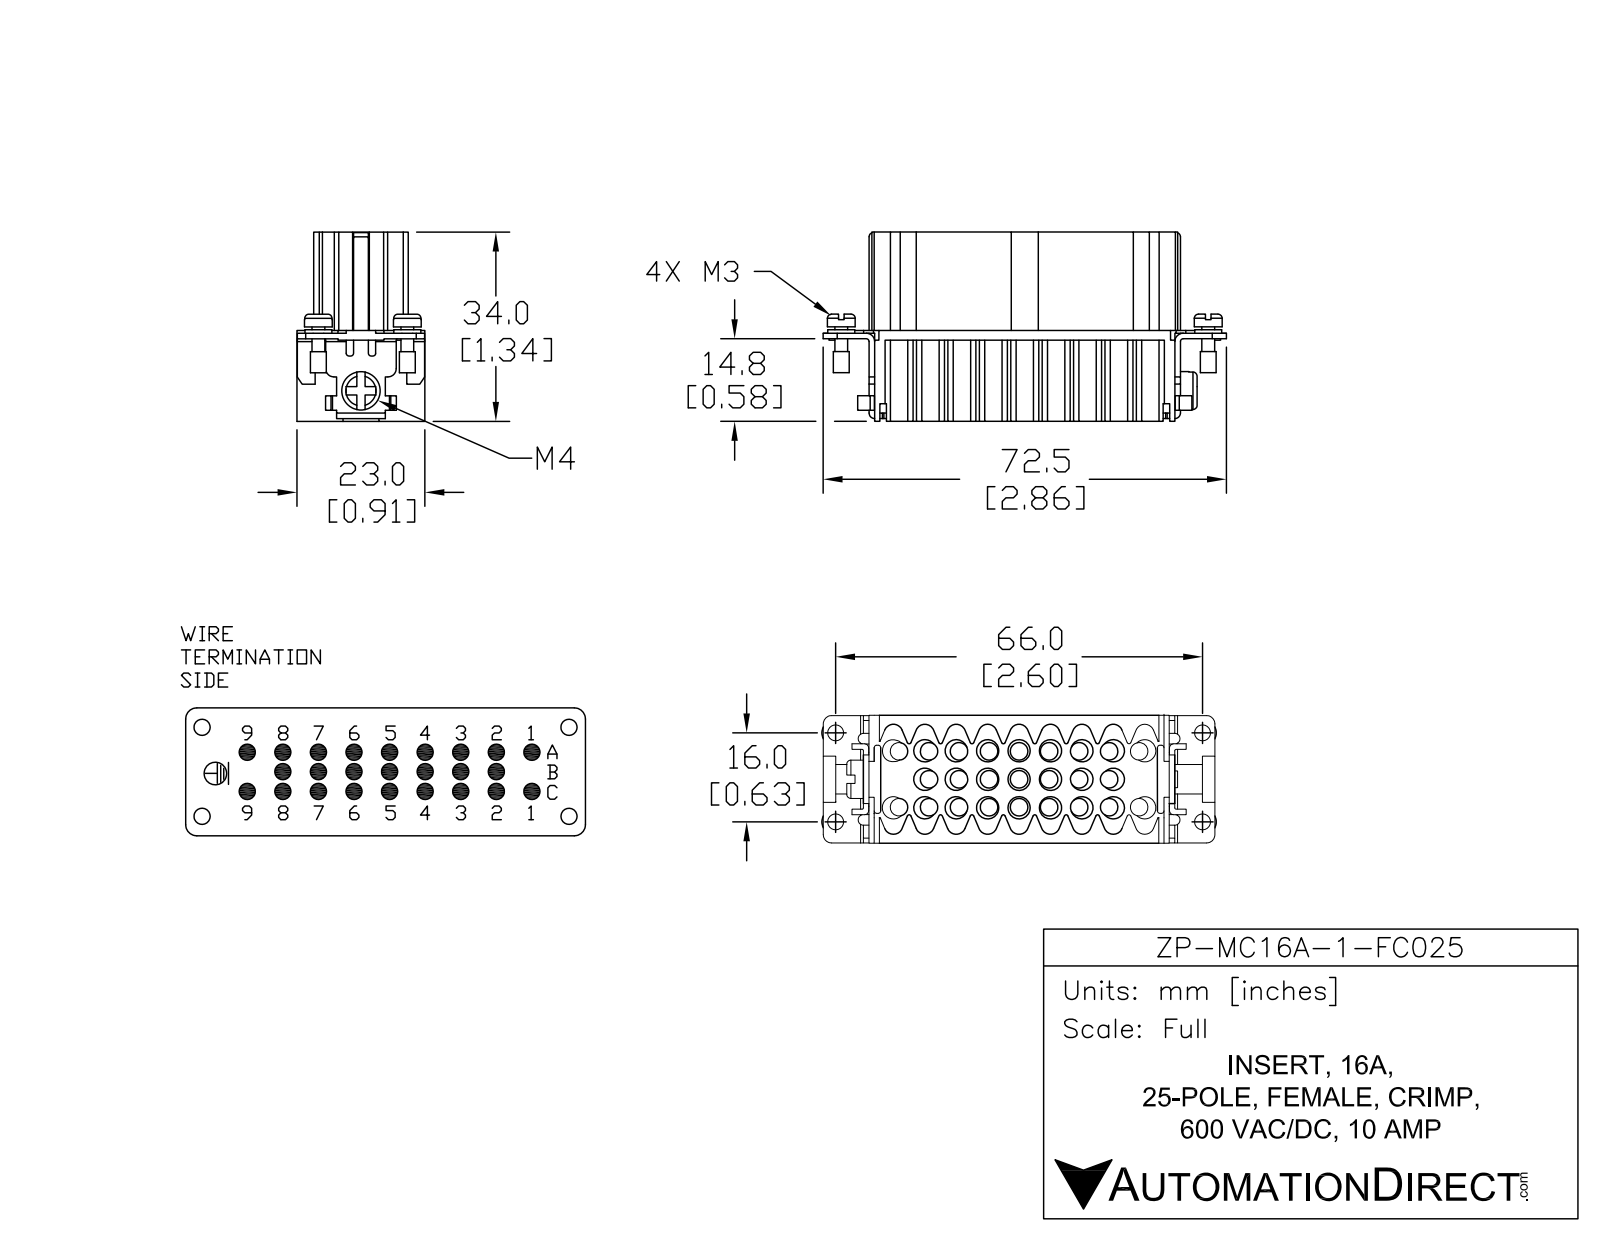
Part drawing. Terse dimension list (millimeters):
name: ZP-MC16A-1-FC025
written by: SolidWorks 2014 (AUTOMOTIVE_DESIGN)
unit: mm
bodies: 2 solids, 725 faces (395 planar, 315 cylindrical, 15 other)
size: 71 × 34.75 × 23
volume: 23 916 mm³; area: 21 634 mm²
holes: 25× ⌀3.15, 15× ⌀4, 11× ⌀5.3, 1× ⌀3
bosses: 4× ⌀5, 4× ⌀4.85, 4× ⌀2.85, 4× ⌀2.3, 1× ⌀6.9
rounds: 18× R1.69, 16× R0.33, 14× R0.25, 12× R1.5, 10× R2, 8× R0.46, 6× R0.5, 6× R0.75
face distances: 5.2, 15.61, 1, 9.76, 10.41, 20.81, 1.75, 14.96, 0.5, 5.85
hole spacings: 7.38, 5.4, 11.91, 10.8, 16.96, 16.2, 11.42, 22.18
